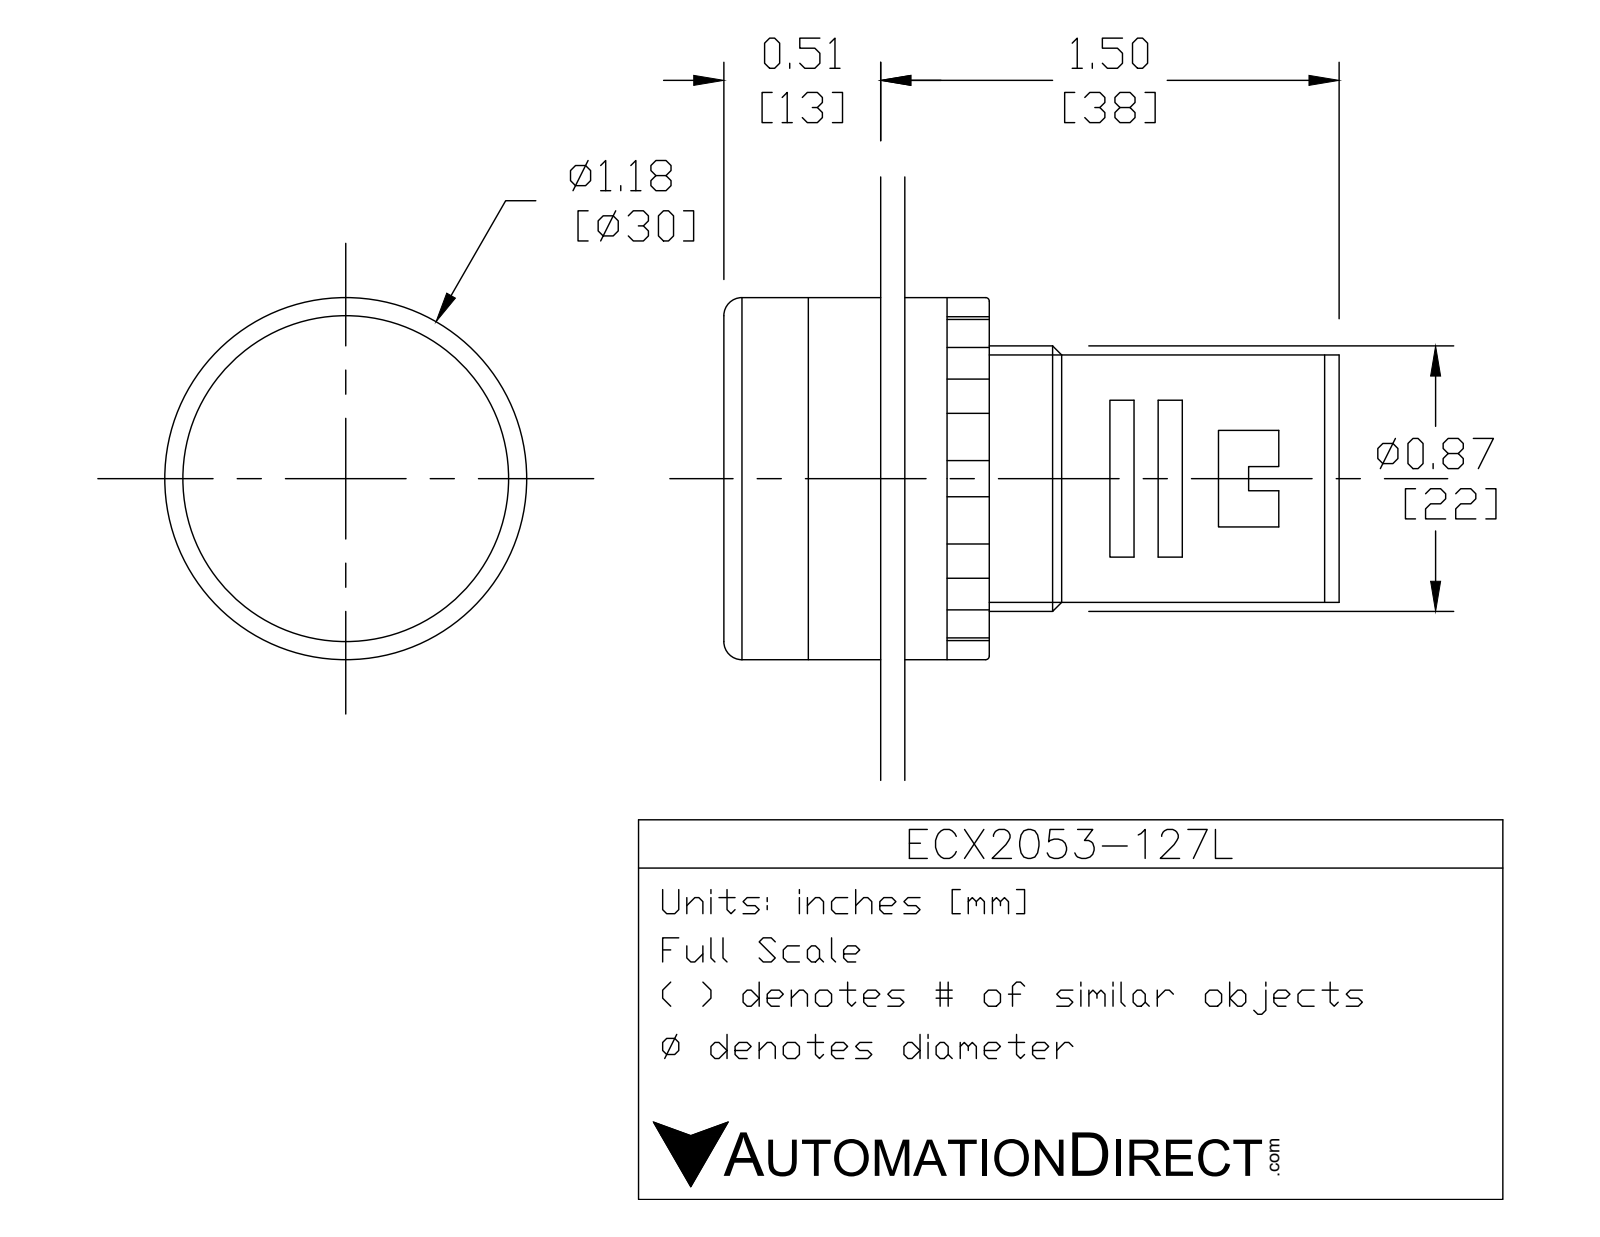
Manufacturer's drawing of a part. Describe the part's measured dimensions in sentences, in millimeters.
The part is named "ECX2053-127L". Its 3-D file was written by "SolidWorks 2017 (AUTOMOTIVE_DESIGN)". It is 6 solids with 123 faces: 63 planar, 39 cylindrical and 21 other. Overall it measures 51 by 30 by 30 millimeters. Its volume is 22 483 cubic millimeters and its surface area 9 831 square millimeters. Round holes: 2 of diameter 5.5, 1 of diameter 22.5. Round bosses or shafts: 2 of diameter 4, 1 of diameter 30, 1 of diameter 29, 1 of diameter 26.5, 1 of diameter 22, 1 of diameter 20. Partial cylindrical surfaces (rounded edges, fillets, slot ends): 12 of radius 1. The main face-to-face distances are 6, 19, 13, 7, 2, 25, 4, 12, 17, 15. The hole center spacings are 4.62, 9.24.
